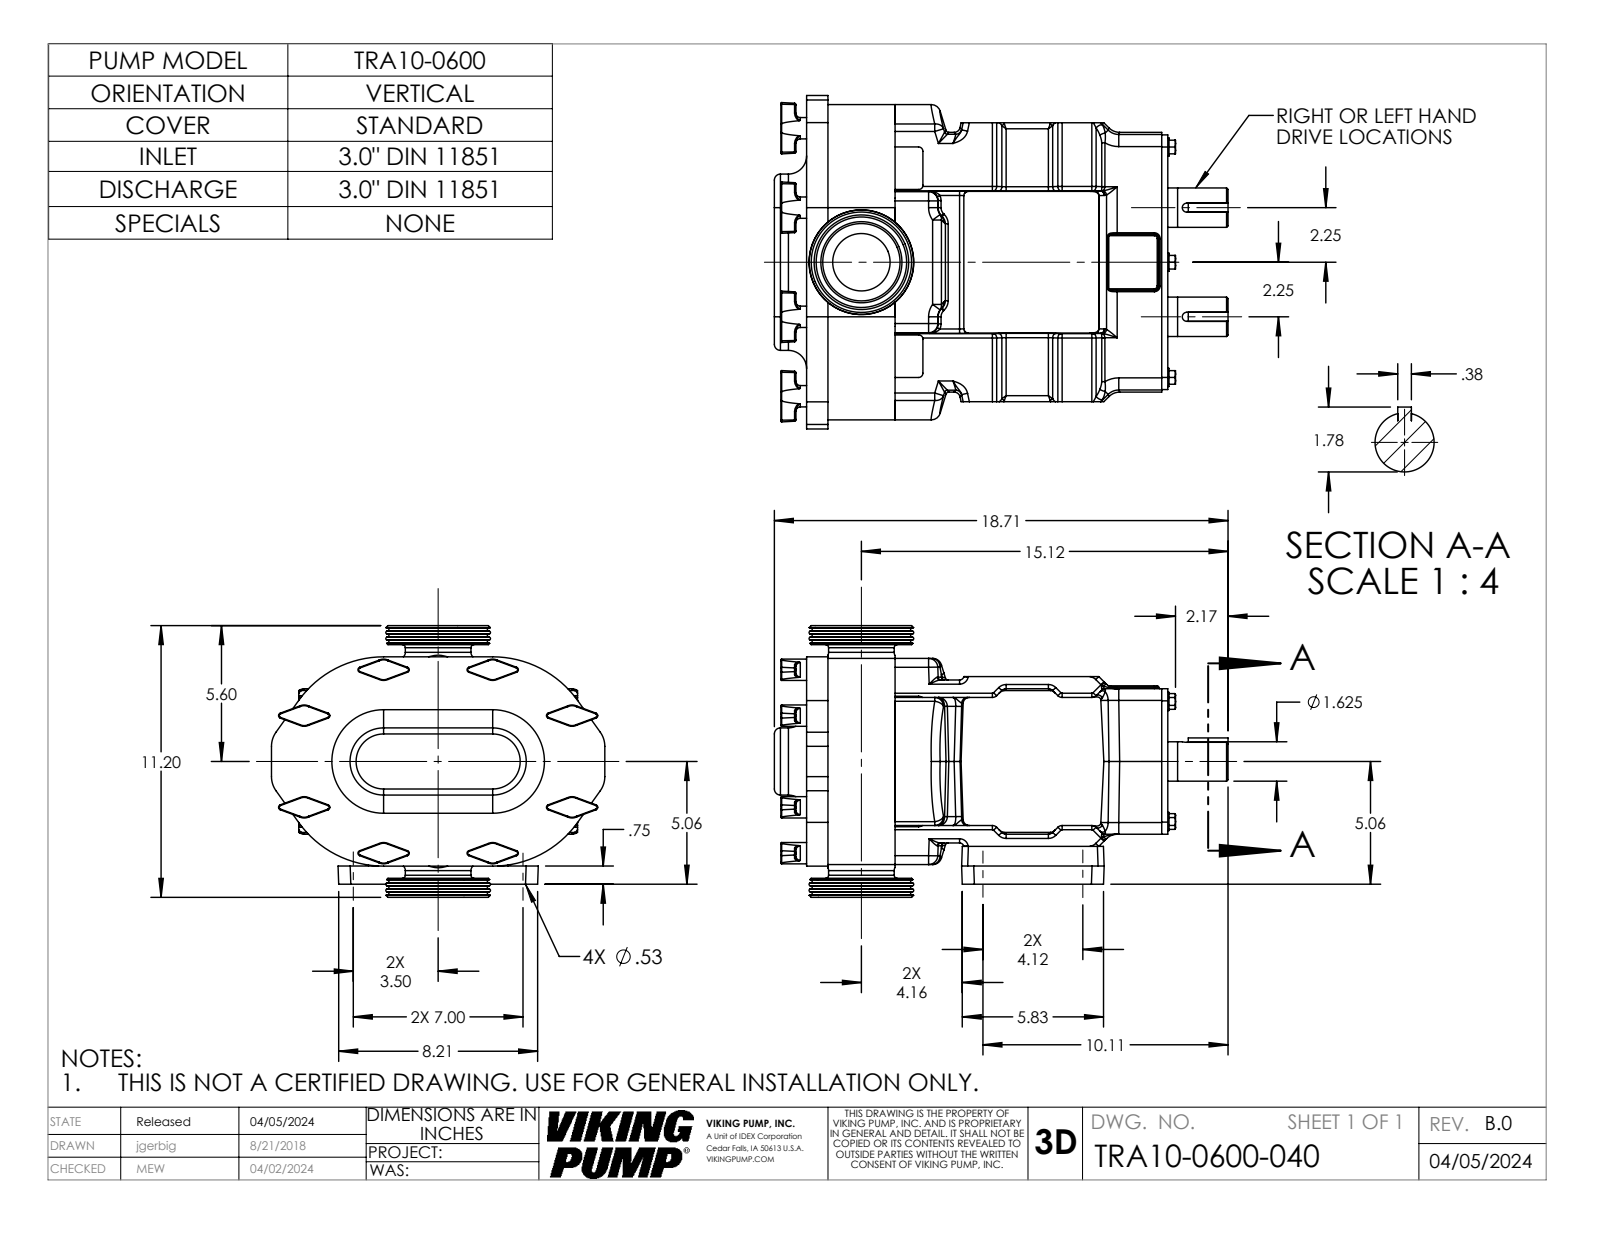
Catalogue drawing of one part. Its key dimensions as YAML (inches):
part_name: "TRA10-0600-BODY; TRA10-0600-GEARBOX-V; TRA10-0600-COVER-STD; 0600DIN11851-30 (+1 more)"
step_written_by: "SolidWorks 2022 (AUTOMOTIVE_DESIGN)"
units: inches
bodies: {solids: 5, faces: 1105, planar: 285, cylindrical: 372, other: 448}
overall_size: [18.714, 13.75, 11.204]
volume: 1191
surface_area: 1392
round_holes:
  - {diameter: 0.531, count: 4}
  - {diameter: 2.368, count: 1}
  - {diameter: 3.732, count: 1}
round_bosses_or_shafts:
  - {diameter: 0.88, count: 8}
  - {diameter: 0.75, count: 6}
  - {diameter: 1.624, count: 2}
  - {diameter: 3.346, count: 1}
  - {diameter: 2.708, count: 1}
partial_cylinders:
  - {radius: 0.18, count: 44}
  - {radius: 0.06, count: 43}
  - {radius: 0.03, count: 32}
  - {radius: 0.25, count: 32}
  - {radius: 0.38, count: 28}
  - {radius: 0.12, count: 24}
  - {radius: 0.5, count: 20}
  - {radius: 0.375, count: 12}
face_to_face_distances: [2.769, 0.88, 3.649, 0.36, 14.899, 14.019, 11.25, 5.64, 0.5, 4.939]
hole_center_spacings: [4.12, 6.115, 7, 8.122, 9.781]
